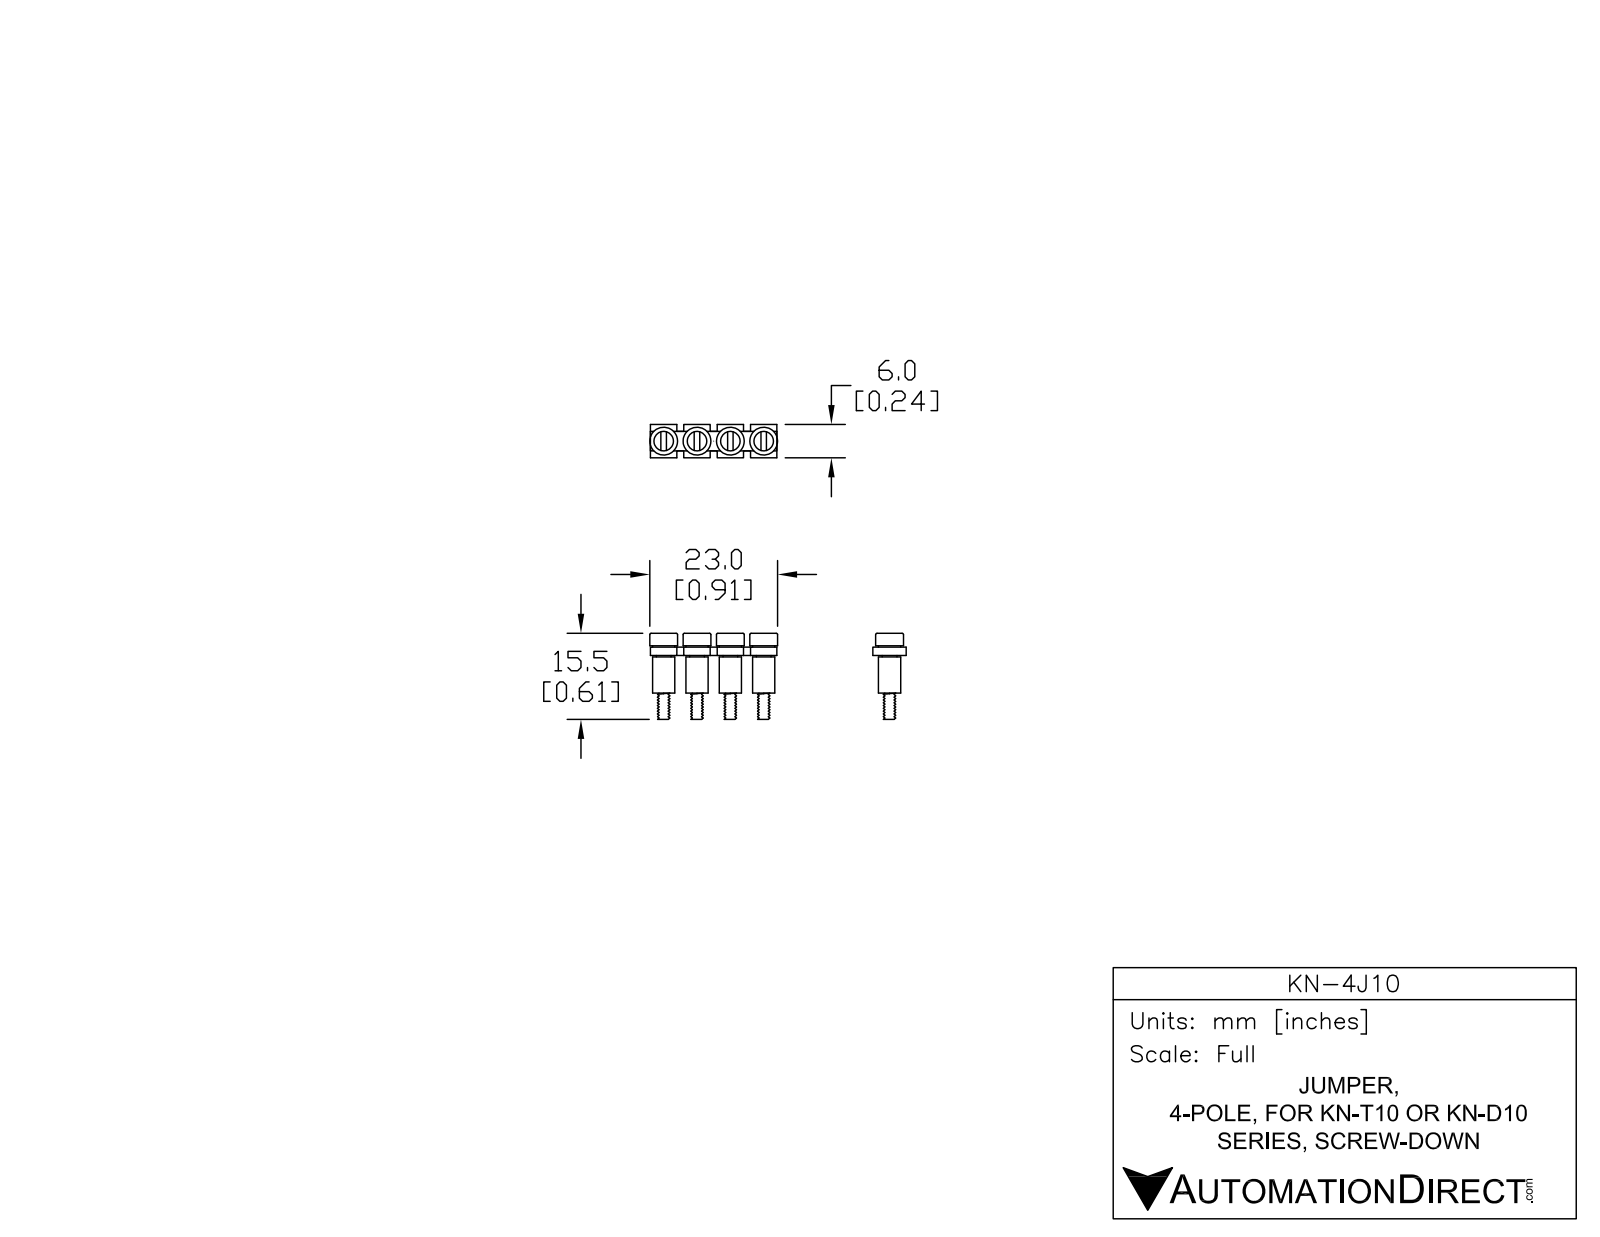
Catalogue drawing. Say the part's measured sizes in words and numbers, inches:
The part is named "KN-4J10". Its 3-D file was written by "SolidWorks 2014 (AUTOMOTIVE_DESIGN)". It is 13 solids with 166 faces: 82 planar, 60 cylindrical and 24 other. Overall it measures 0.906 by 0.61 by 0.236 inches. Its volume is 0.044 cubic inches and its surface area 3.077 square inches. Round holes: 4 of diameter 0.118, 4 of diameter 0.124, 4 of diameter 0.138. Round bosses or shafts: 4 of diameter 0.197, 4 of diameter 0.157, 4 of diameter 0.104. The main face-to-face distances are 0.059, 0.069, 0.236, 0.079, 0.039, 0.187, 0.098, 0.138, 0.423, 0.472. The hole center spacings are 0.236, 0.472, 0.709.
